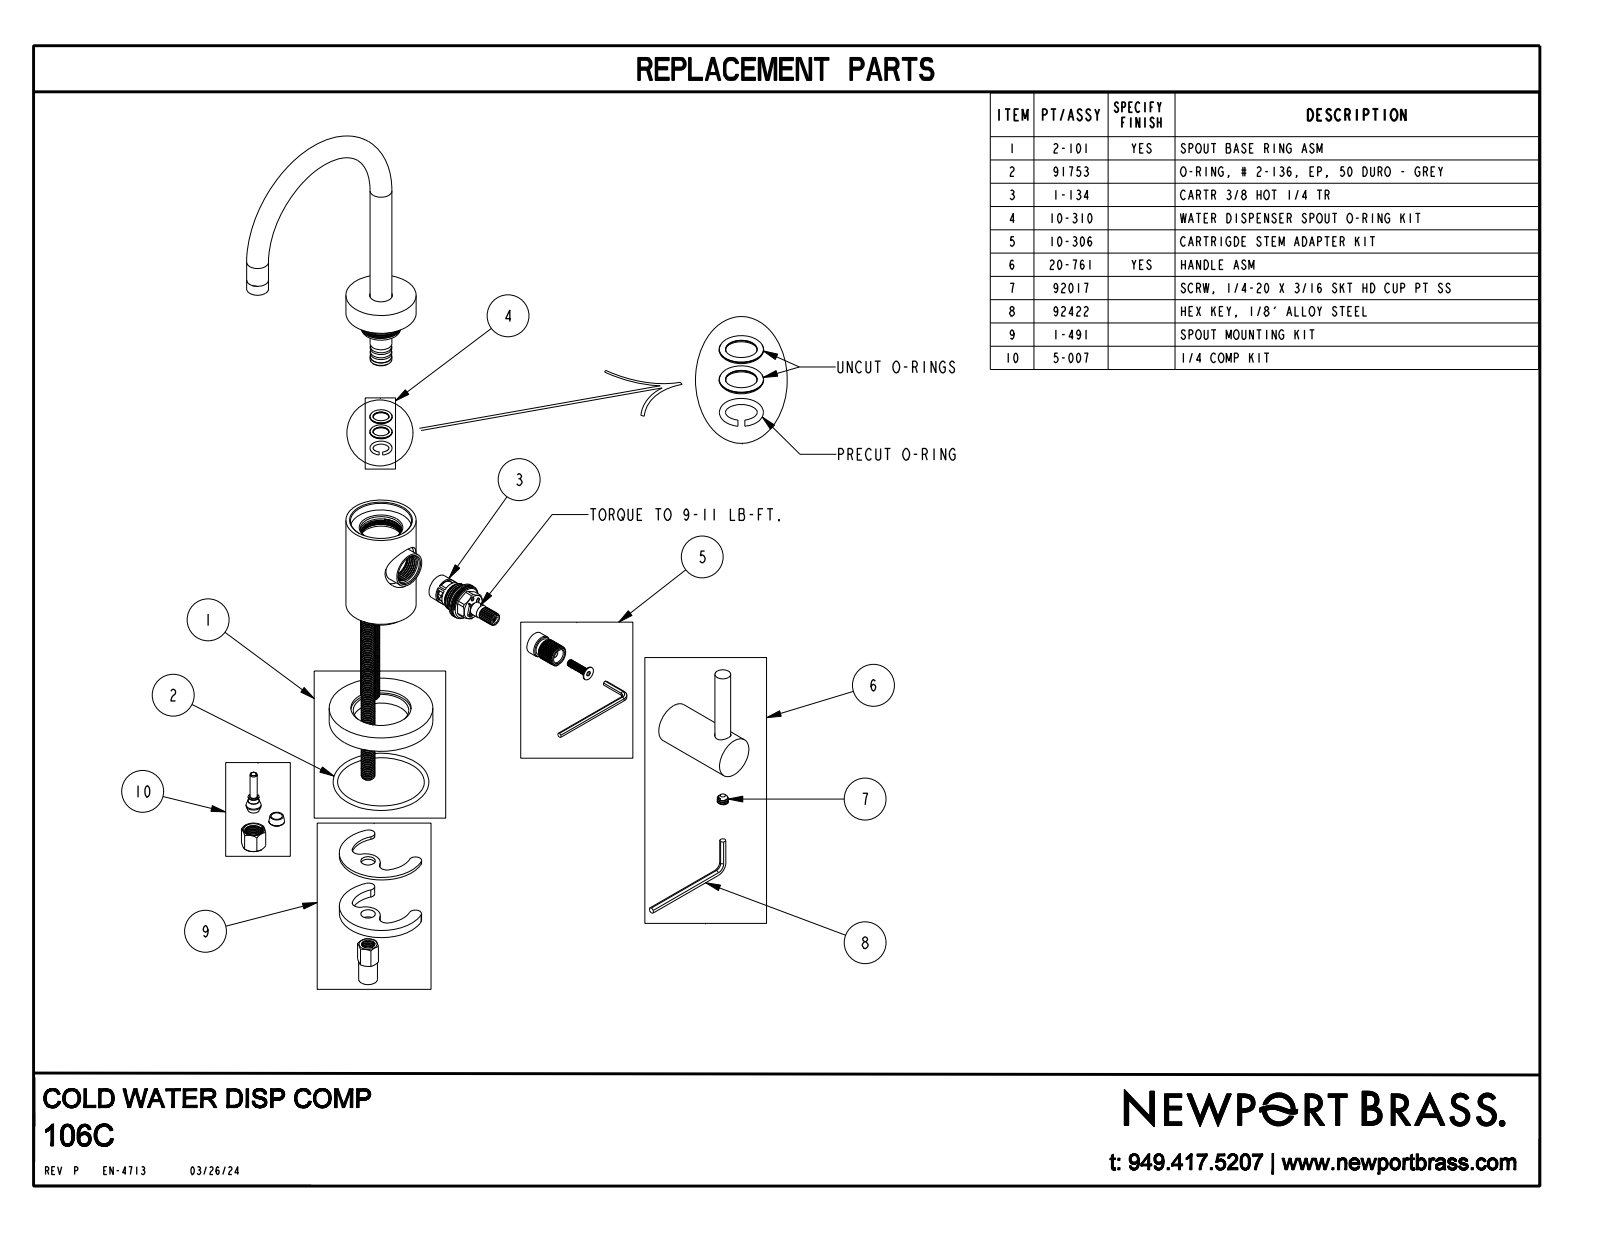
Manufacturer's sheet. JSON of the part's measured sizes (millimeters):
{"part_name": "106C", "step_written_by": "CREO PARAMETRIC BY PTC INC, 2018400 (CONFIG_CONTROL_DESIGN)", "units": "millimeters", "bodies": {"solids": 1, "faces": 23, "planar": 7, "cylindrical": 14, "other": 2}, "overall_size": [234.3, 138.1, 95.3], "volume_mm3": 178100, "surface_area_mm2": 32750, "round_holes": [[25.4, 1]], "round_bosses_or_shafts": [[12.7, 2], [60.3, 1], [40.9, 1], [24.1, 1], [9.1, 1]], "face_to_face_distances": [9.5, 80.6, 71.1, 164.4, 154.9, 83.8, 98.8, 89.3, 18.2, 65.6]}
